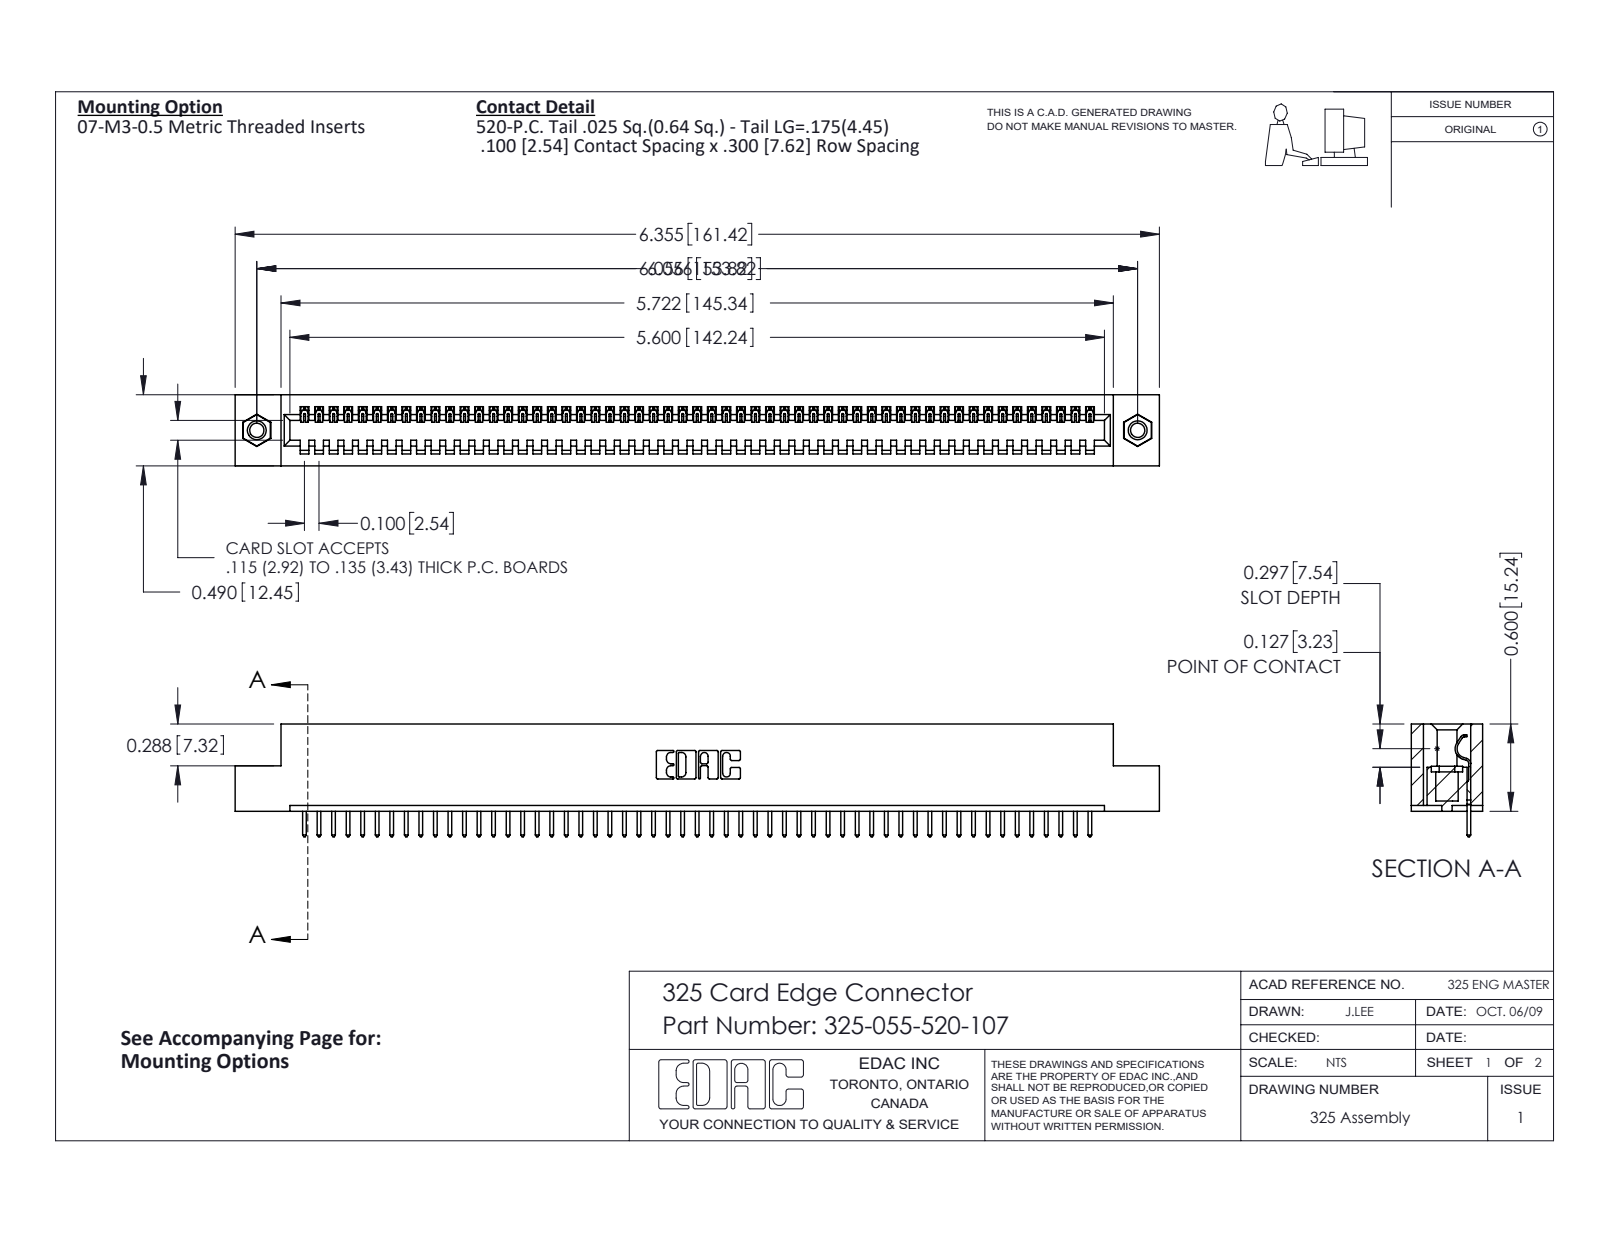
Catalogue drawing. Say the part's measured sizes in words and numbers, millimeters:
The part is named "325-055-520-107; 325-292-001_325-293-120; 345-250-001_345-250-005-103; 325 Part_TI". Its 3-D file was written by "SolidWorks 2016 (CONFIG_CONTROL_DESIGN)". It is 58 solids with 3364 faces: 2412 planar, 936 cylindrical and 16 other. Overall it measures 161.4 by 19.7 by 12.4 millimeters. Its volume is 20 430 cubic millimeters and its surface area 22 000 square millimeters. Round holes: 2 of diameter 2.5, 2 of diameter 3.2, 2 of diameter 4.1. Round bosses or shafts: 2 of diameter 3.9. Partial cylindrical surfaces (rounded edges, fillets, slot ends): 110 of radius 0.2, 110 of radius 0.3, 22 of radius 0.3, 6 of radius 0.2, 6 of radius 0.8, 3 of radius 0.7, 1 of radius 0.4, 1 of radius 0.6. The main face-to-face distances are 2.1, 10.3, 12.4, 7.6, 2.7, 9.7, 0.6, 8.3, 6.7, 14.2. The hole center spacings are 153.8.
